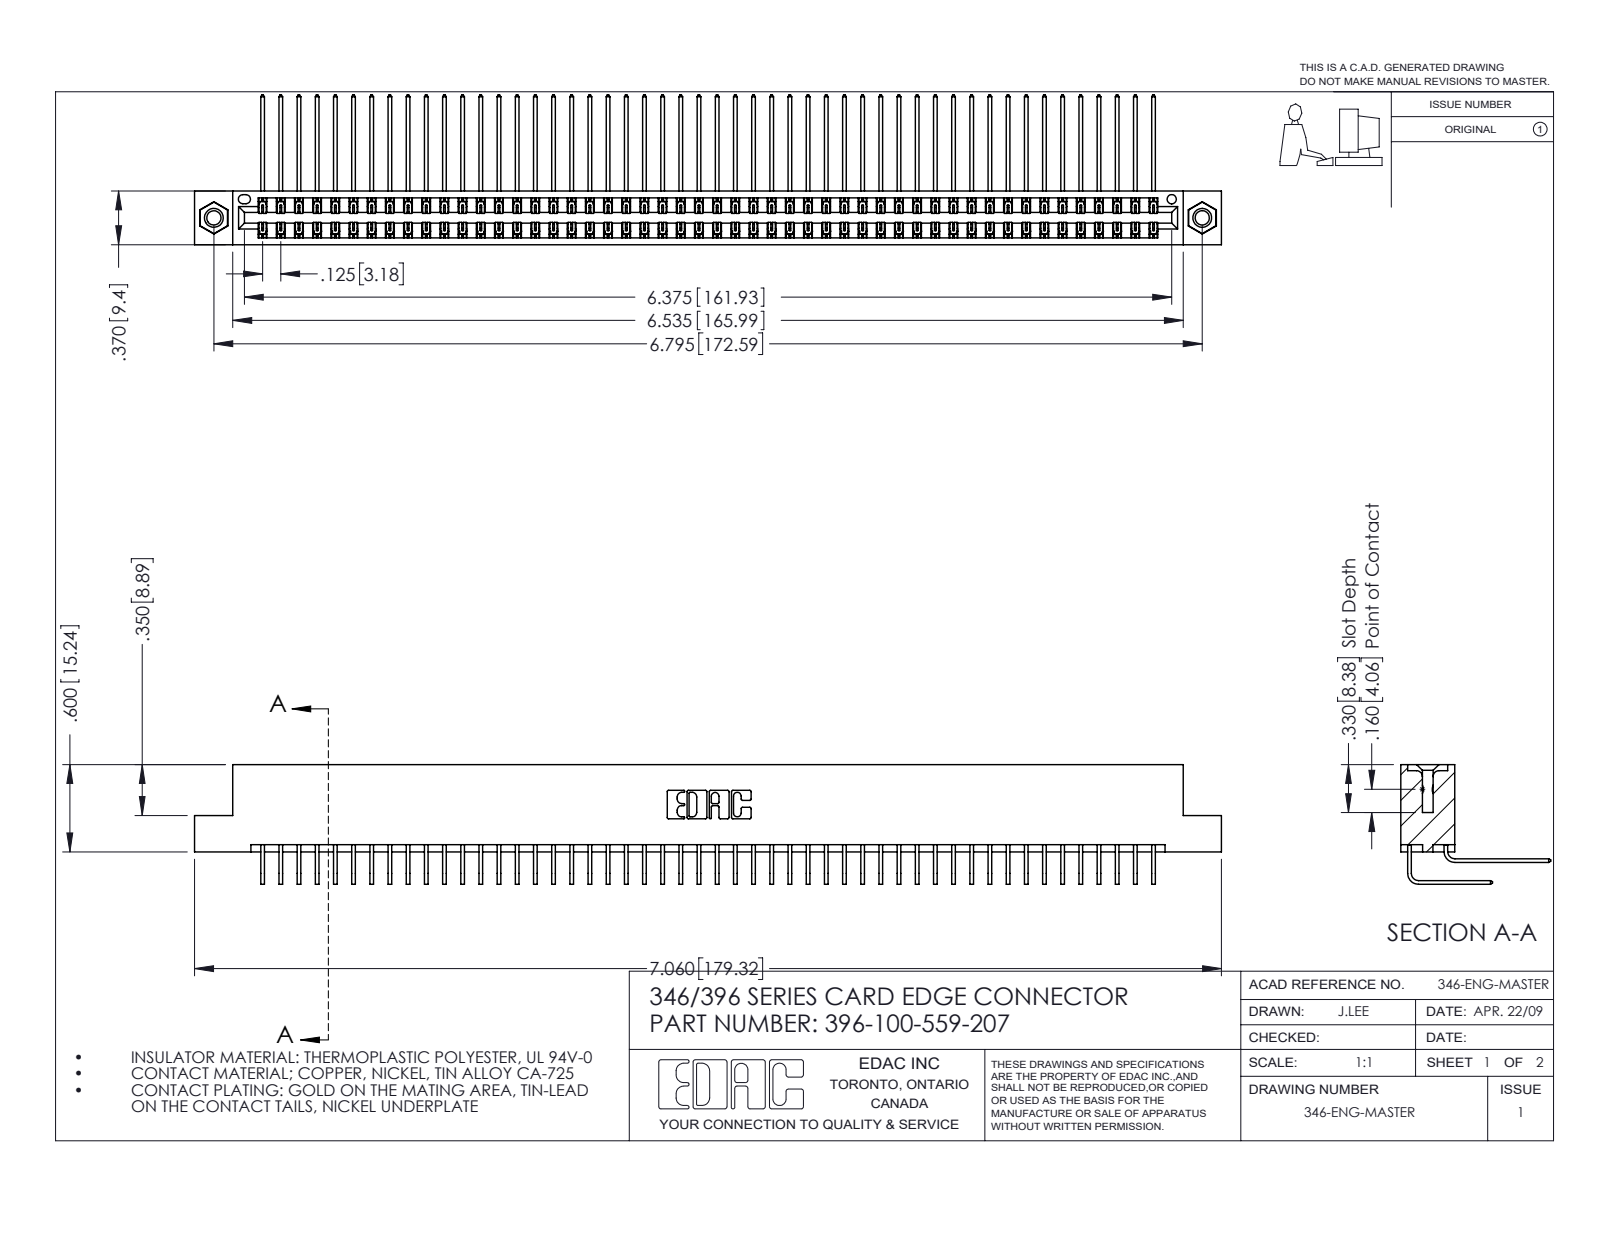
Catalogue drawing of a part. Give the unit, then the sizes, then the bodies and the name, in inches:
Units: inches
Overall size (bounding box): 7.06 × 1.03 × 0.823
Round holes (diameter × count): ⌀0.098 ×2, ⌀0.125 ×2, ⌀0.156 ×2, ⌀0.064 ×1
Round bosses / shafts (diameter × count): ⌀0.155 ×2
Partial cylindrical surfaces — rounded edges, fillets, slot ends (radius × count): R0.006 ×150, R0.01 ×22, R0.007 ×6, R0.031 ×6, R0.026 ×3, R0.014 ×2, R0.022 ×2, R0.024 ×2
Main face-to-face distances: 0.048, 0.322, 0.025, 0.37, 0.25, 0.072, 0.298, 0.275, 0.148, 0.222
Hole centre spacings: 0.246, 6.586, 6.795
Volume: 1.105 in³ · Surface area: 43.13 in²
Bodies: 103 solids, 5582 faces (3808 planar, 1758 cylindrical, 16 other)
Part name (STEP PRODUCT): 345-292-001_558 559 Tail - 1; 396-100-559-207; 345-250-001_345-250-005-103; 346 Part_Flush Mounting Lugs - 0.156 Dia-TI (+1 more)
STEP written by: SolidWorks 2016 (CONFIG_CONTROL_DESIGN)
